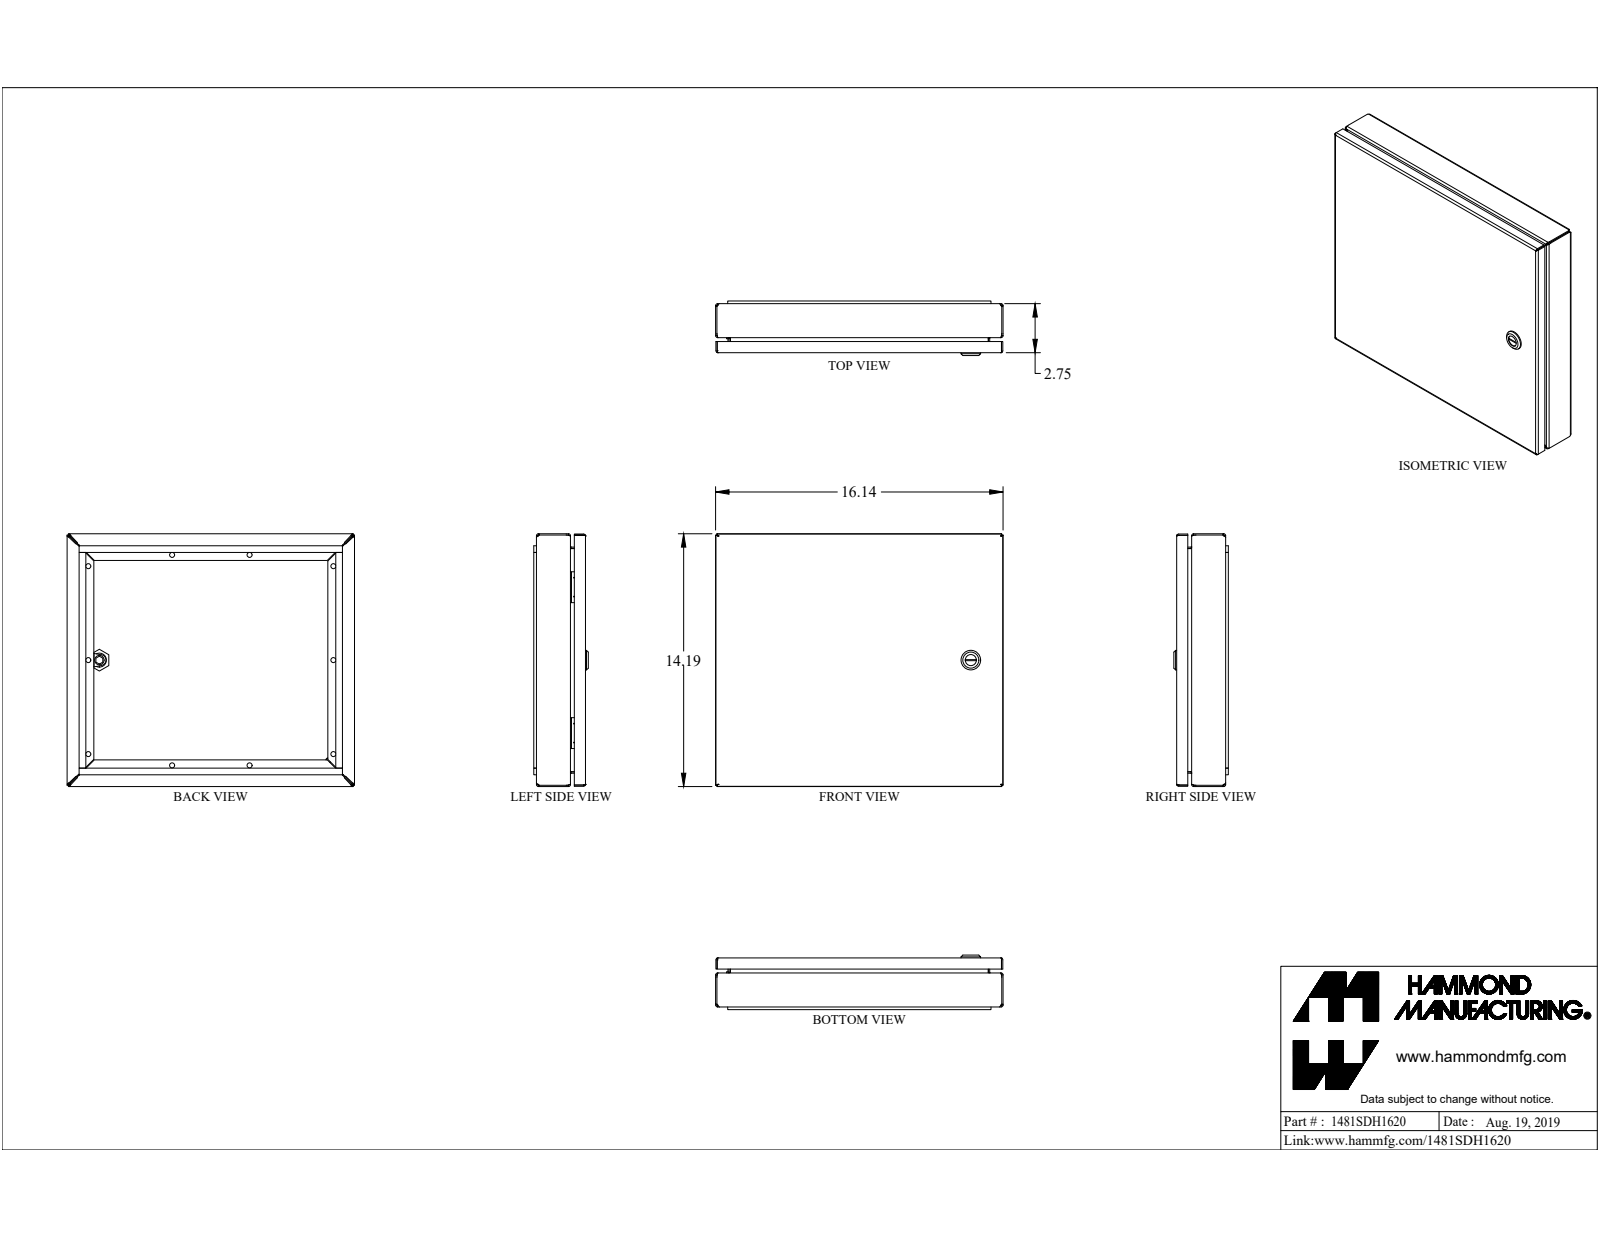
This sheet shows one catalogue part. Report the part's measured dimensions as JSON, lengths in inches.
{"part_name": "1481SDH1620", "step_written_by": "SolidWorks 2019 (CONFIG_CONTROL_DESIGN)", "units": "inches", "bodies": {"solids": 23, "faces": 616, "planar": 348, "cylindrical": 170, "other": 98}, "overall_size": [16.14, 14.19, 3.061], "volume_in3": 49.56, "surface_area_in2": 1290, "round_holes": [[0.281, 10], [0.172, 1], [0.232, 1], [0.24, 1], [0.242, 1], [0.625, 1], [0.785, 1]], "round_bosses_or_shafts": [[1.1, 1], [0.525, 1], [0.455, 1], [0.398, 1], [0.356, 1], [0.313, 1], [0.292, 1], [0.25, 1]], "partial_cylinders_radius": [[0.036, 28], [0.108, 28], [0.382, 12], [19.003, 8], [0.006, 4], [0.062, 4], [0.25, 4], [0.499, 4]], "face_to_face_distances": [0.072, 2.579, 0.843, 1.736, 2.651, 14.118, 16.068, 2.507, 2.679, 1.836], "hole_center_spacings": [4.75, 5.273, 7.554, 9.078, 10.813, 12.131, 14.388, 14.739]}
